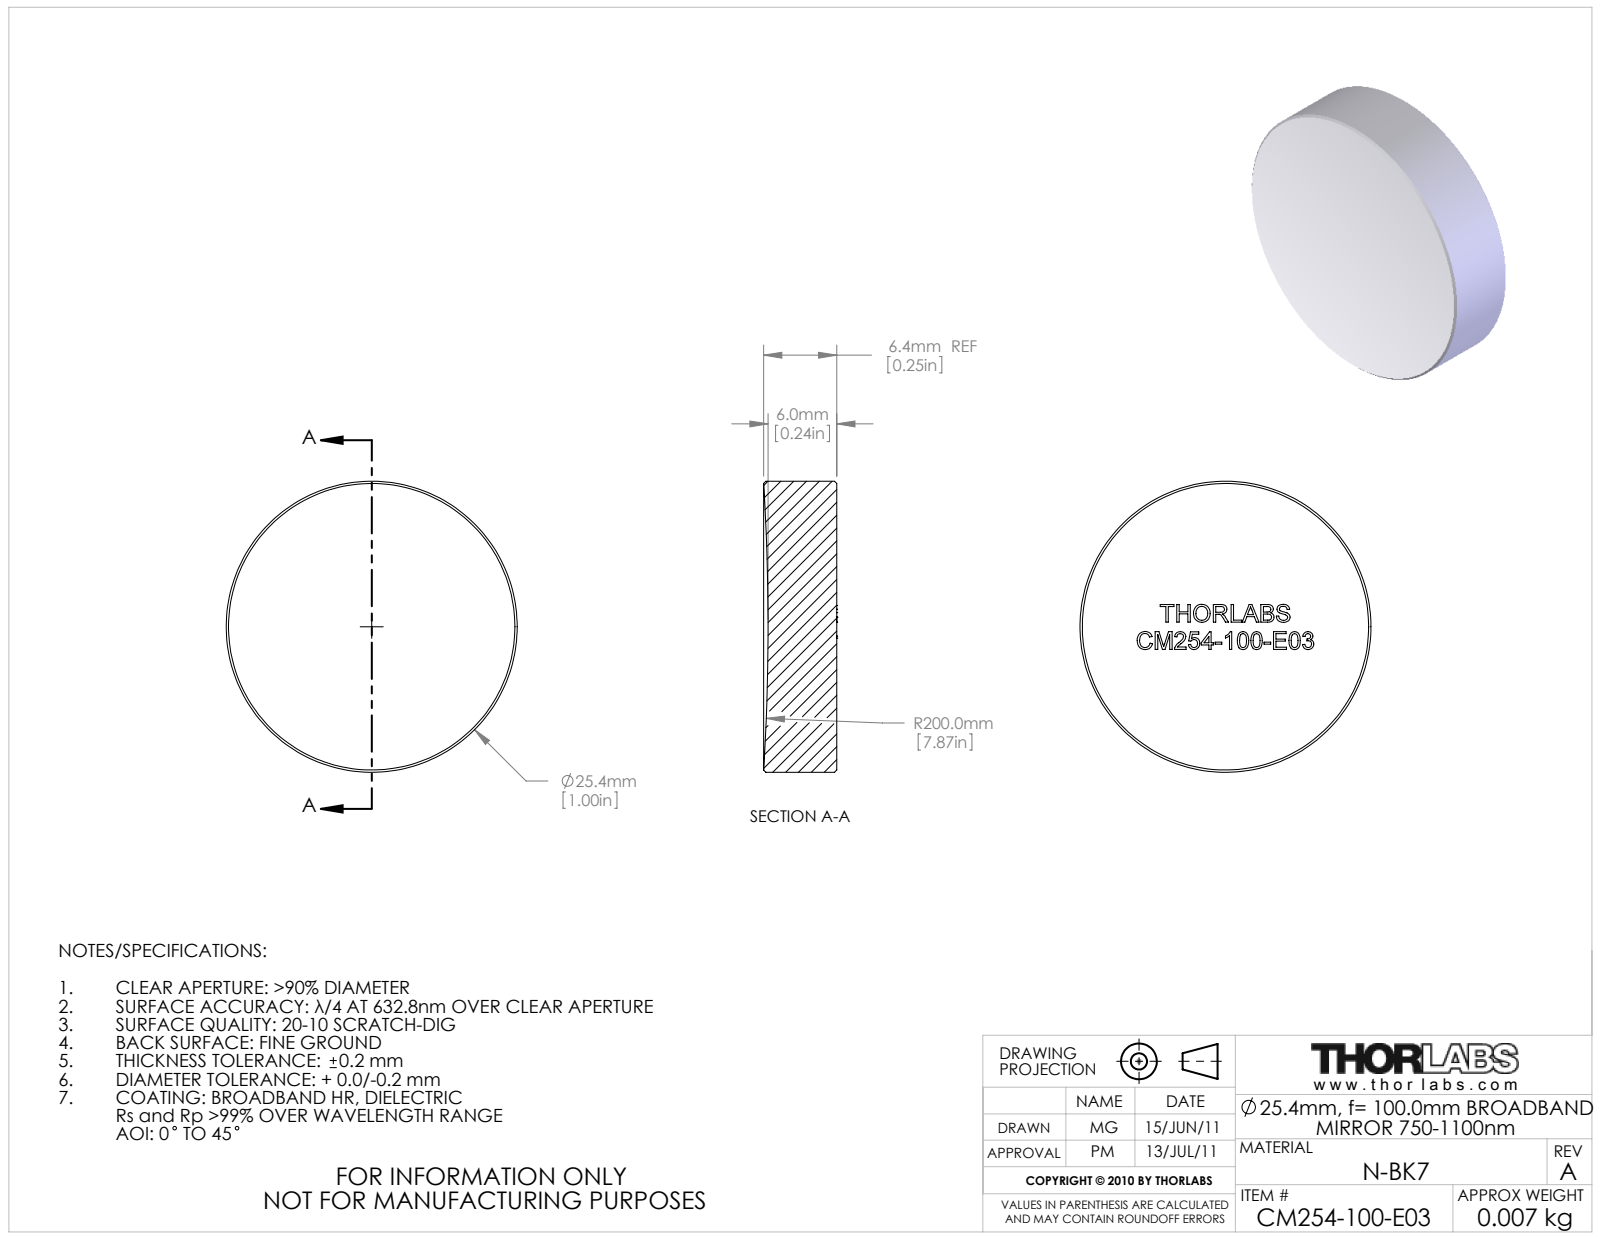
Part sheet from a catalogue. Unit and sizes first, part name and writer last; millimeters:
Units: millimetres
Overall size (bounding box): 25.4 × 25.4 × 6.39
Round bosses / shafts (diameter × count): ⌀25.4 ×1
Main face-to-face distances: 2.55
Bodies: 0 solids, 48 faces (33 planar, 2 cylindrical, 13 other)
Part name (STEP PRODUCT): 22644-E0W
STEP written by: SolidWorks 2011 (AUTOMOTIVE_DESIGN)
